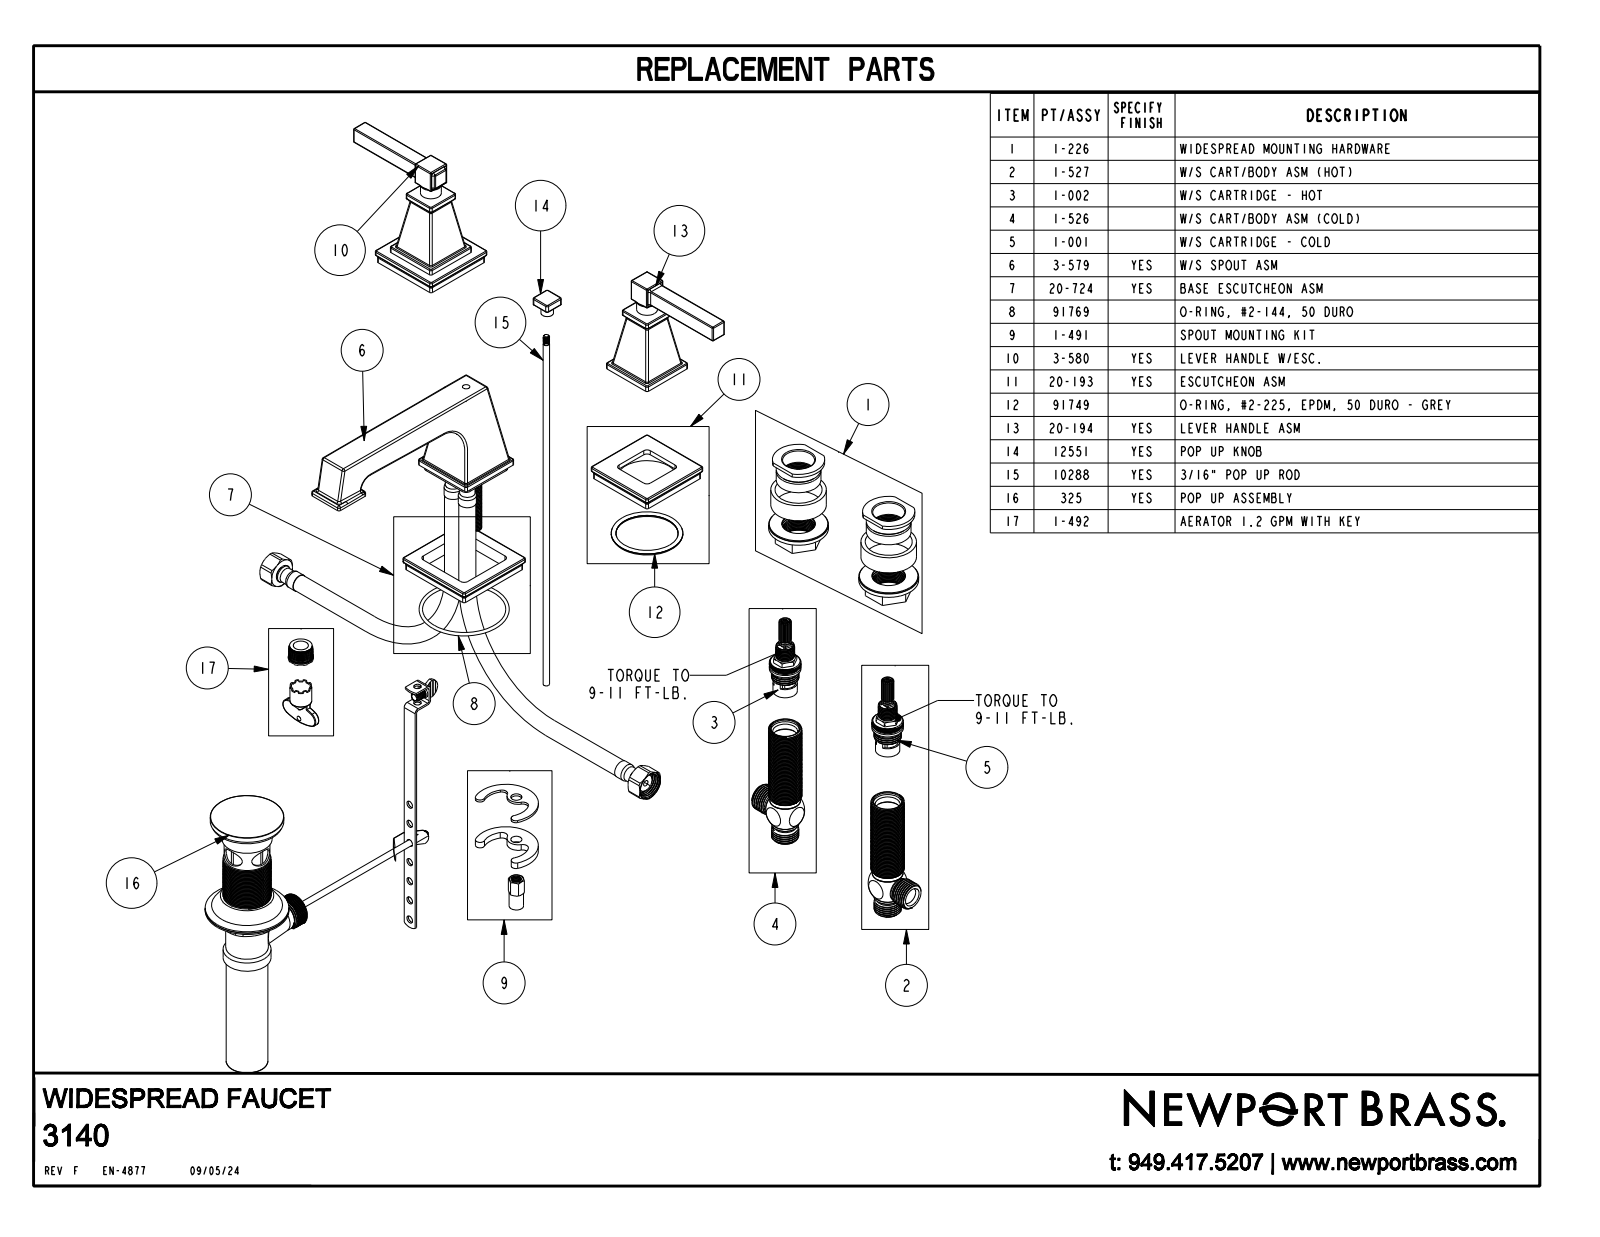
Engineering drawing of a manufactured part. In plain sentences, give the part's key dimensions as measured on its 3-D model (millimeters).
The part is named "3140". Its 3-D file was written by "CREO PARAMETRIC BY PTC INC, 2018400 (CONFIG_CONTROL_DESIGN)". It is 3 solids with 672 faces: 126 planar, 274 cylindrical and 272 other. Overall it measures 357.2 by 184.9 by 96.5 millimeters. Its volume is 441 600 cubic millimeters and its surface area 77 680 square millimeters. Round bosses or shafts: 2 of diameter 15.9, 2 of diameter 12.9, 1 of diameter 9.5. Partial cylindrical surfaces (rounded edges, fillets, slot ends): 101 of radius 1.5, 100 of radius 0.8, 16 of radius 2.3, 8 of radius 5.8, 2 of radius 25.4, 1 of radius 9.5, 1 of radius 19.1. The main face-to-face distances are 10.4, 82.6, 72.1, 12.7, 63.5, 200.2, 4.6, 53.1, 19.1, 15.1.
